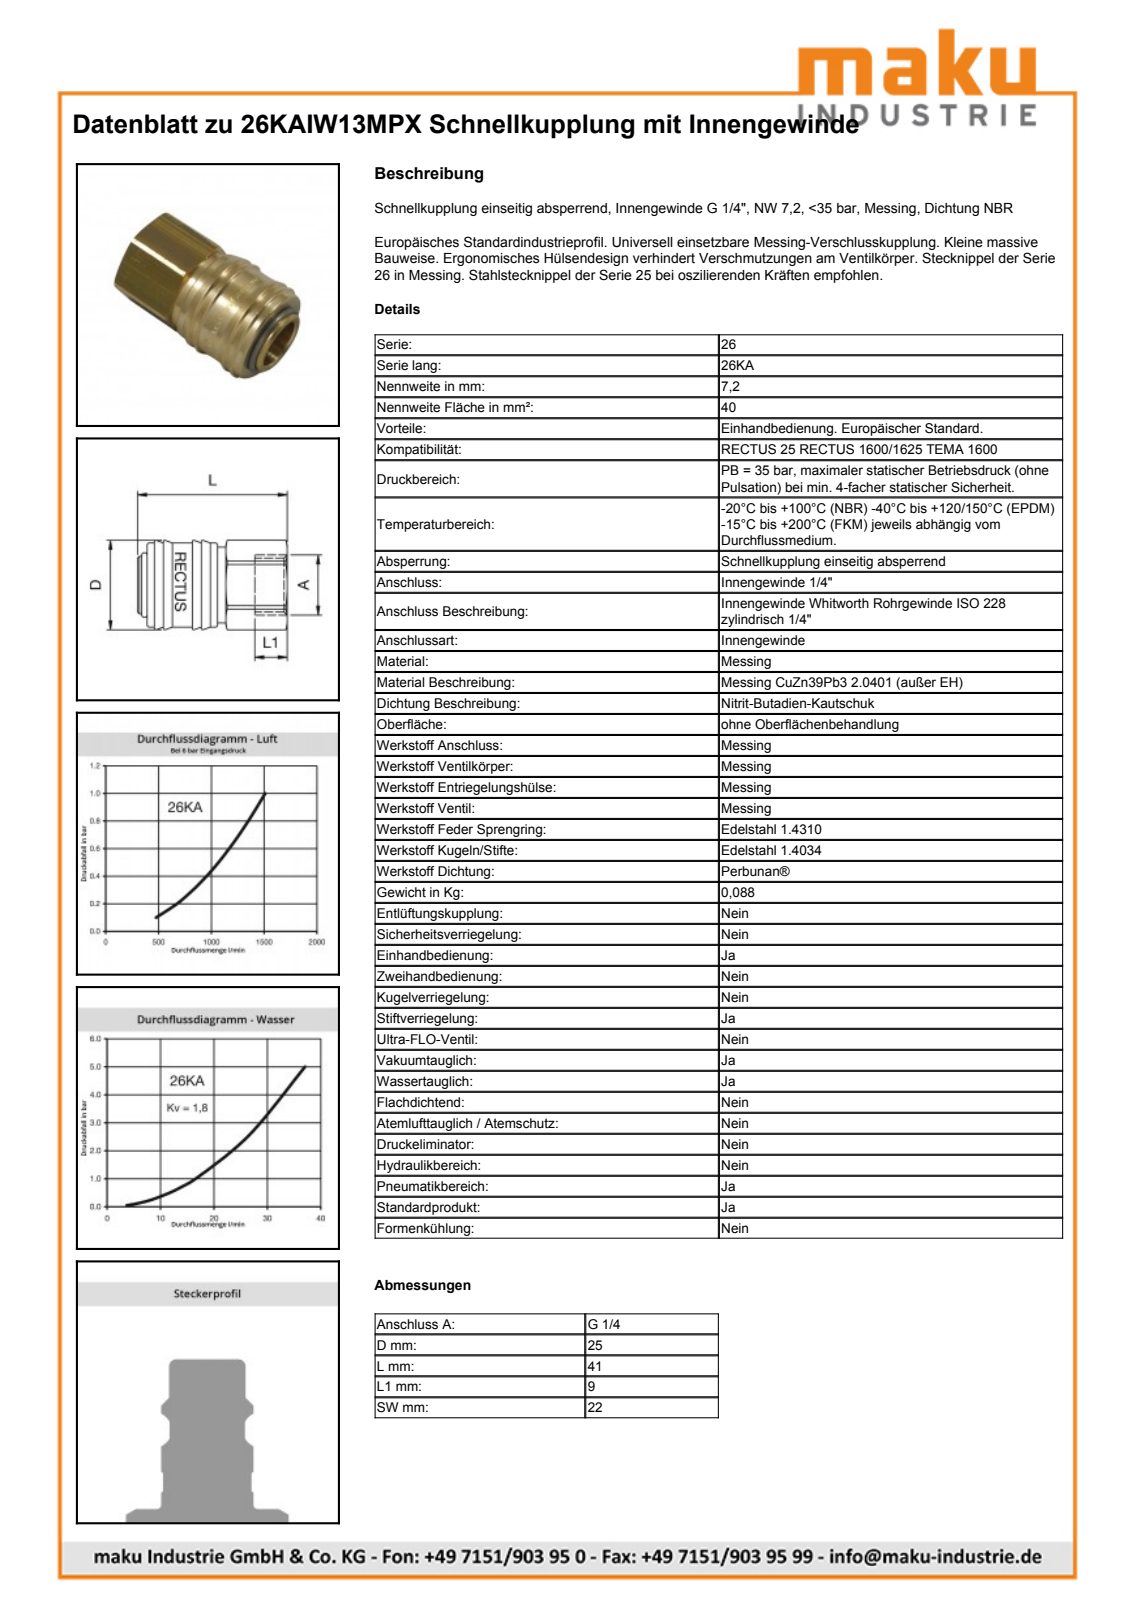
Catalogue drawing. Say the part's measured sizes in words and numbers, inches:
The part is named "D110056". Its 3-D file was written by "Autodesk Inventor 2013 (AUTOMOTIVE_DESIGN)". It is 2 solids with 461 faces: 175 planar, 62 cylindrical and 224 other. Overall it measures 1.618 by 0.976 by 0.976 inches. Its volume is 0.842 cubic inches and its surface area 12.37 square inches. Round holes: 1 of diameter 0.451, 1 of diameter 0.569, 1 of diameter 0.608, 1 of diameter 0.634, 1 of diameter 0.669, 1 of diameter 0.831. Round bosses or shafts: 1 of diameter 0.917, 1 of diameter 0.827, 1 of diameter 0.709, 1 of diameter 0.656, 1 of diameter 0.628, 1 of diameter 0.604, 1 of diameter 0.589. Partial cylindrical surfaces (rounded edges, fillets, slot ends): 1 of radius 0.455, 1 of radius 0.486. The main face-to-face distances are 0.866, 0.437, 1.077, 1.514, 0.104, 1.181, 1.618, 0.827, 0.722, 0.354.
